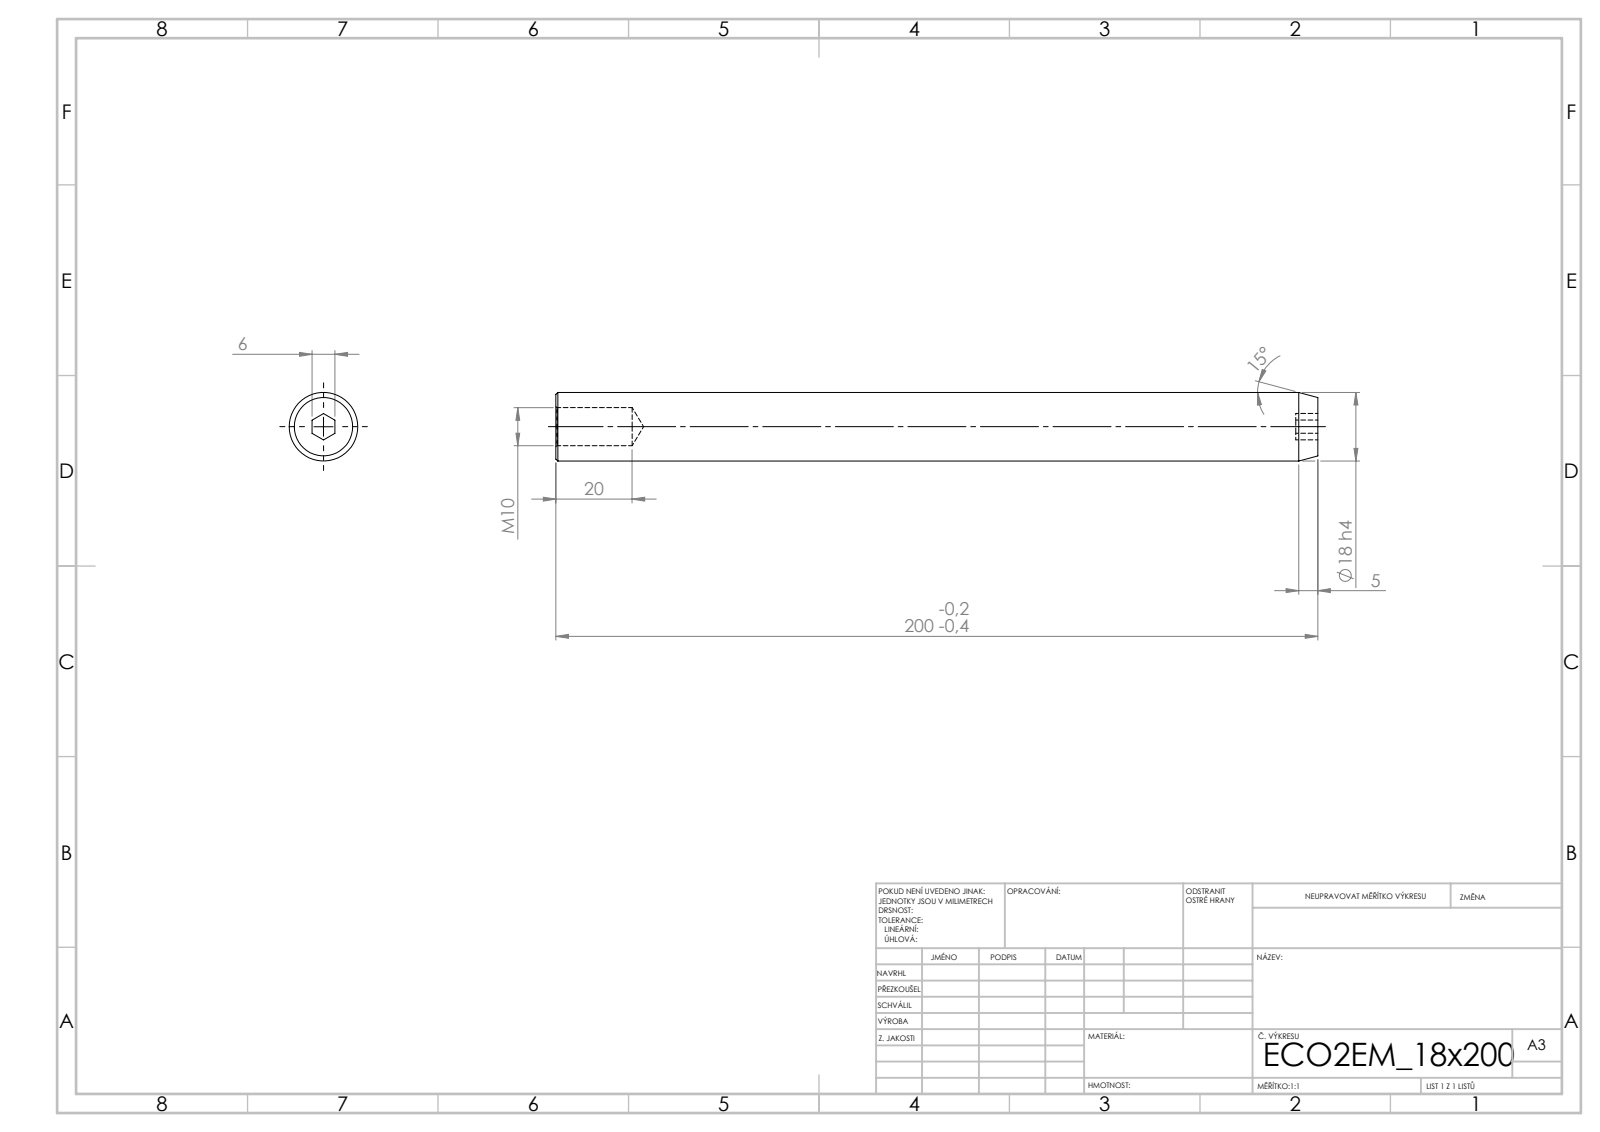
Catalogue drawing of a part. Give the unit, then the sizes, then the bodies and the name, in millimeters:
Units: millimetres
Overall size (bounding box): 200 × 18 × 18
Round holes (diameter × count): ⌀10 ×1
Round bosses / shafts (diameter × count): ⌀18 ×1
Main face-to-face distances: 200, 6, 5.8, 194.2
Volume: 48 876 mm³ · Surface area: 12 478 mm²
Bodies: 1 solid, 21 faces (9 planar, 4 cylindrical, 8 other)
STEP written by: SolidWorks 2019 (CONFIG_CONTROL_DESIGN)
